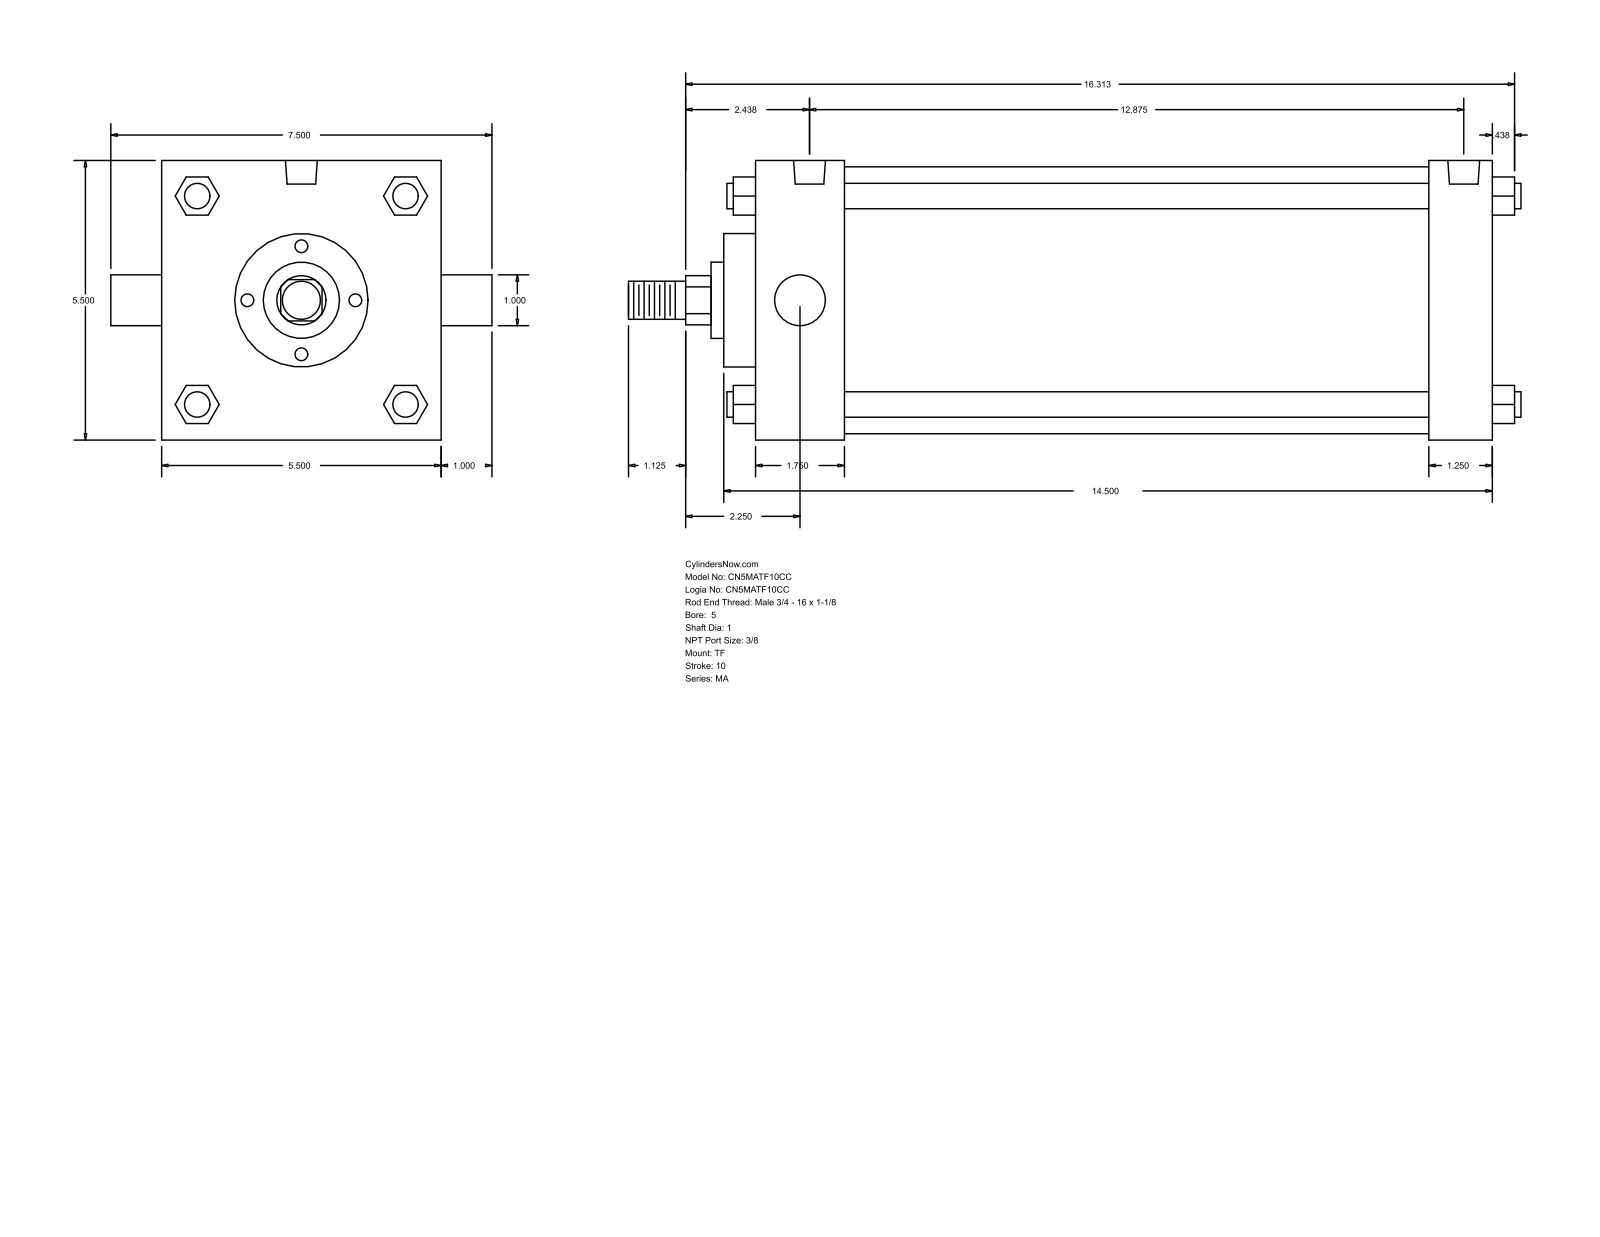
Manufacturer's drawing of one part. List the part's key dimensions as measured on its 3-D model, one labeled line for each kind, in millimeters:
Part name (STEP PRODUCT): MA_TF__0500_1
STEP written by: GSSL Pune (CONFIG_CONTROL_DESIGN)
Units: millimetres
Bodies: 0 solids, 122 faces (93 planar, 29 cylindrical, 0 other)
Overall size (bounding box): 446.09 × 190.5 × 139.7
Round holes (diameter × count): ⌀11.11 ×3, ⌀15.93 ×2
Round bosses / shafts (diameter × count): ⌀12.7 ×4, ⌀25.4 ×2, ⌀133.35 ×1, ⌀66.67 ×1, ⌀38.1 ×1, ⌀19.05 ×1
Partial cylindrical surfaces — rounded edges, fillets, slot ends (radius × count): R12.29 ×1
Main face-to-face distances: 139.7, 368.31, 336.56, 31.75, 44.46, 292.1, 323.85, 15.87, 60.33, 352.43
Hole centre spacings: 4.76, 322.27, 317.51, 327.03
